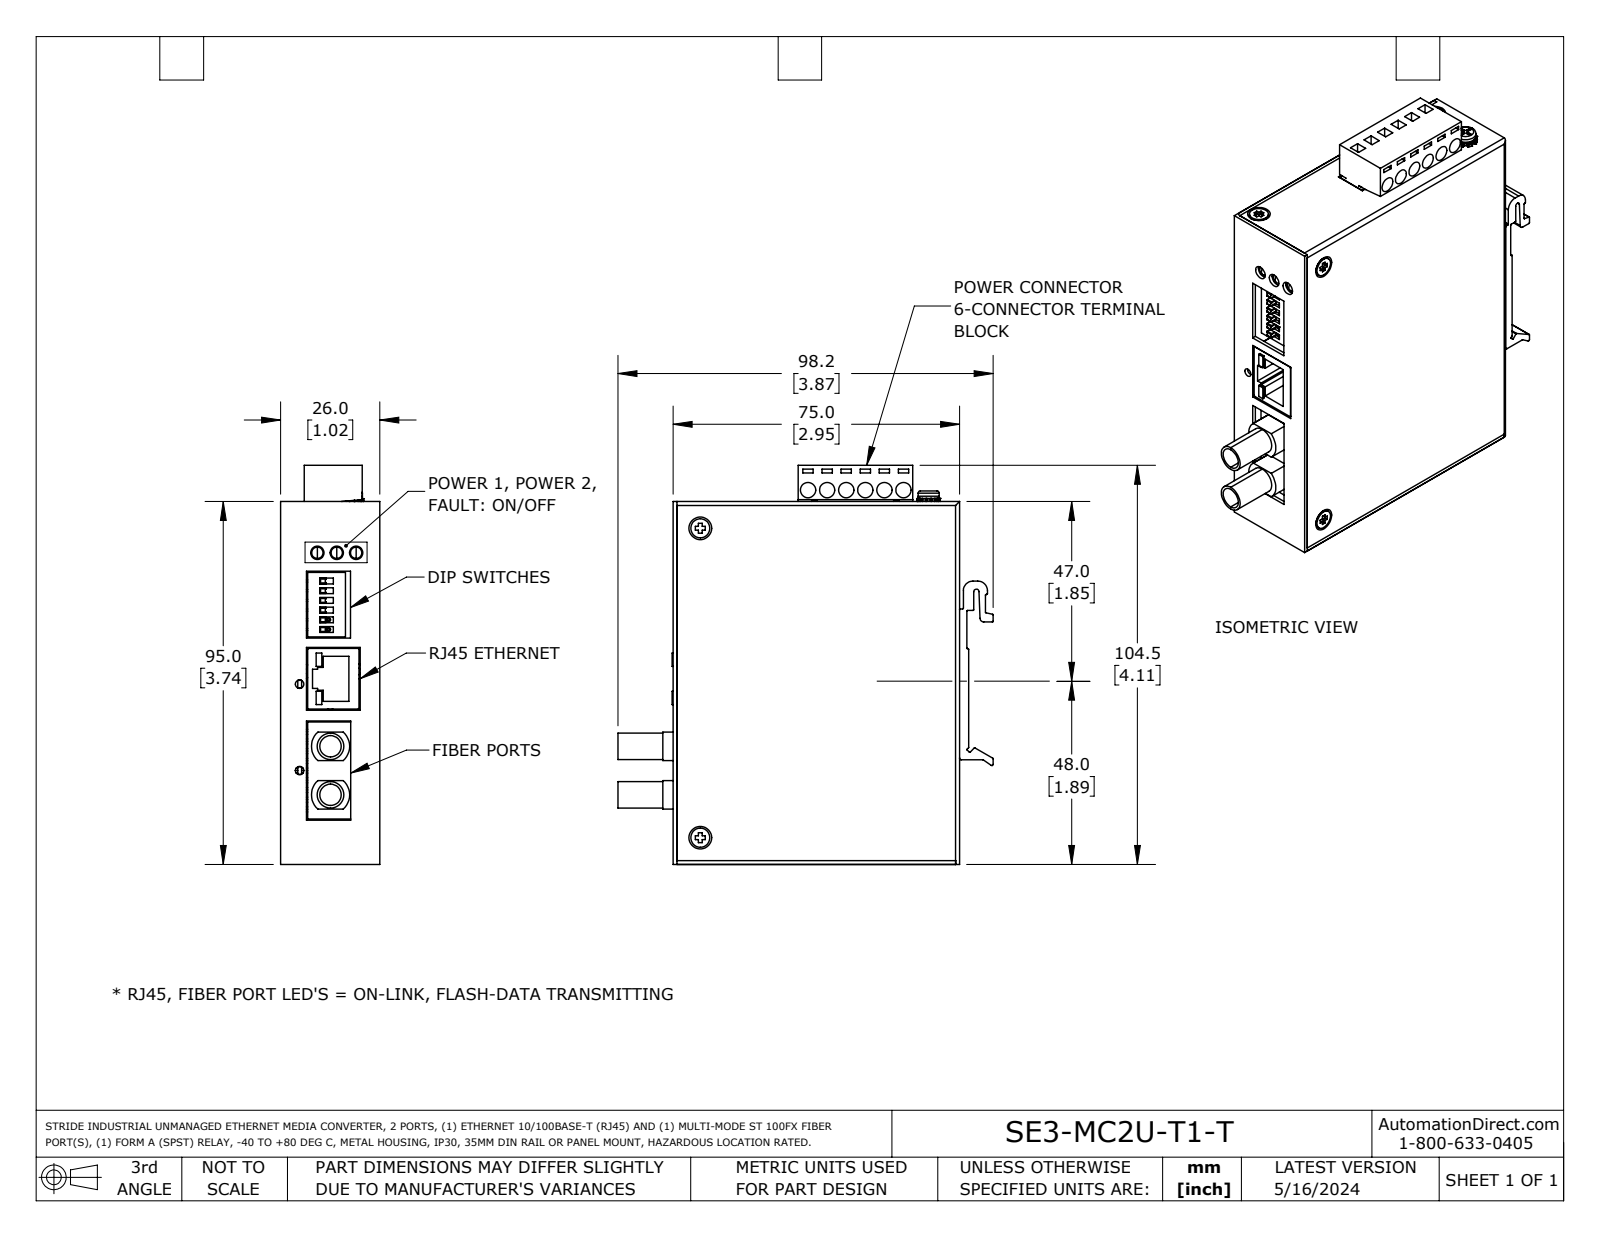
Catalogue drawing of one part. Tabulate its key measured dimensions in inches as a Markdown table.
| quantity | value |
| --- | --- |
| part name | SE3-MC2U-T1-T |
| STEP written by | SolidWorks 2023 (AUTOMOTIVE_DESIGN) |
| units | inches |
| bodies | 22 solids, 1695 faces (1104 planar, 400 cylindrical, 191 other) |
| overall size | 4.114 × 3.868 × 1.024 |
| volume | 2.735 in³ |
| surface area | 107.7 in² |
| round holes (diameter × count) | 0.157 × 15, 0.079 × 7, 0.118 × 7, 0.138 × 3, 0.087 × 2, 0.22 × 2, 0.059 × 1 |
| round bosses / shafts (diameter × count) | 0.051 × 11, 0.197 × 9, 0.094 × 9, 0.02 × 6, 0.11 × 5, 0.157 × 4, 0.118 × 3, 0.274 × 2 |
| partial cylindrical surfaces (radius × count) | 0.004 × 77, 0.008 × 41, 0.024 × 12, 0.02 × 11, 0.034 × 6, 0.118 × 6, 0.138 × 4, 0.012 × 3 |
| main face-to-face distances | 0.039, 0.984, 1.024, 0.02, 0.945, 2.913, 1.004, 0.965, 3.701, 2.953 |
| hole center spacings | 0.197, 0.394, 0.591, 0.406, 0.787, 2.953, 0.2, 0.405 |
